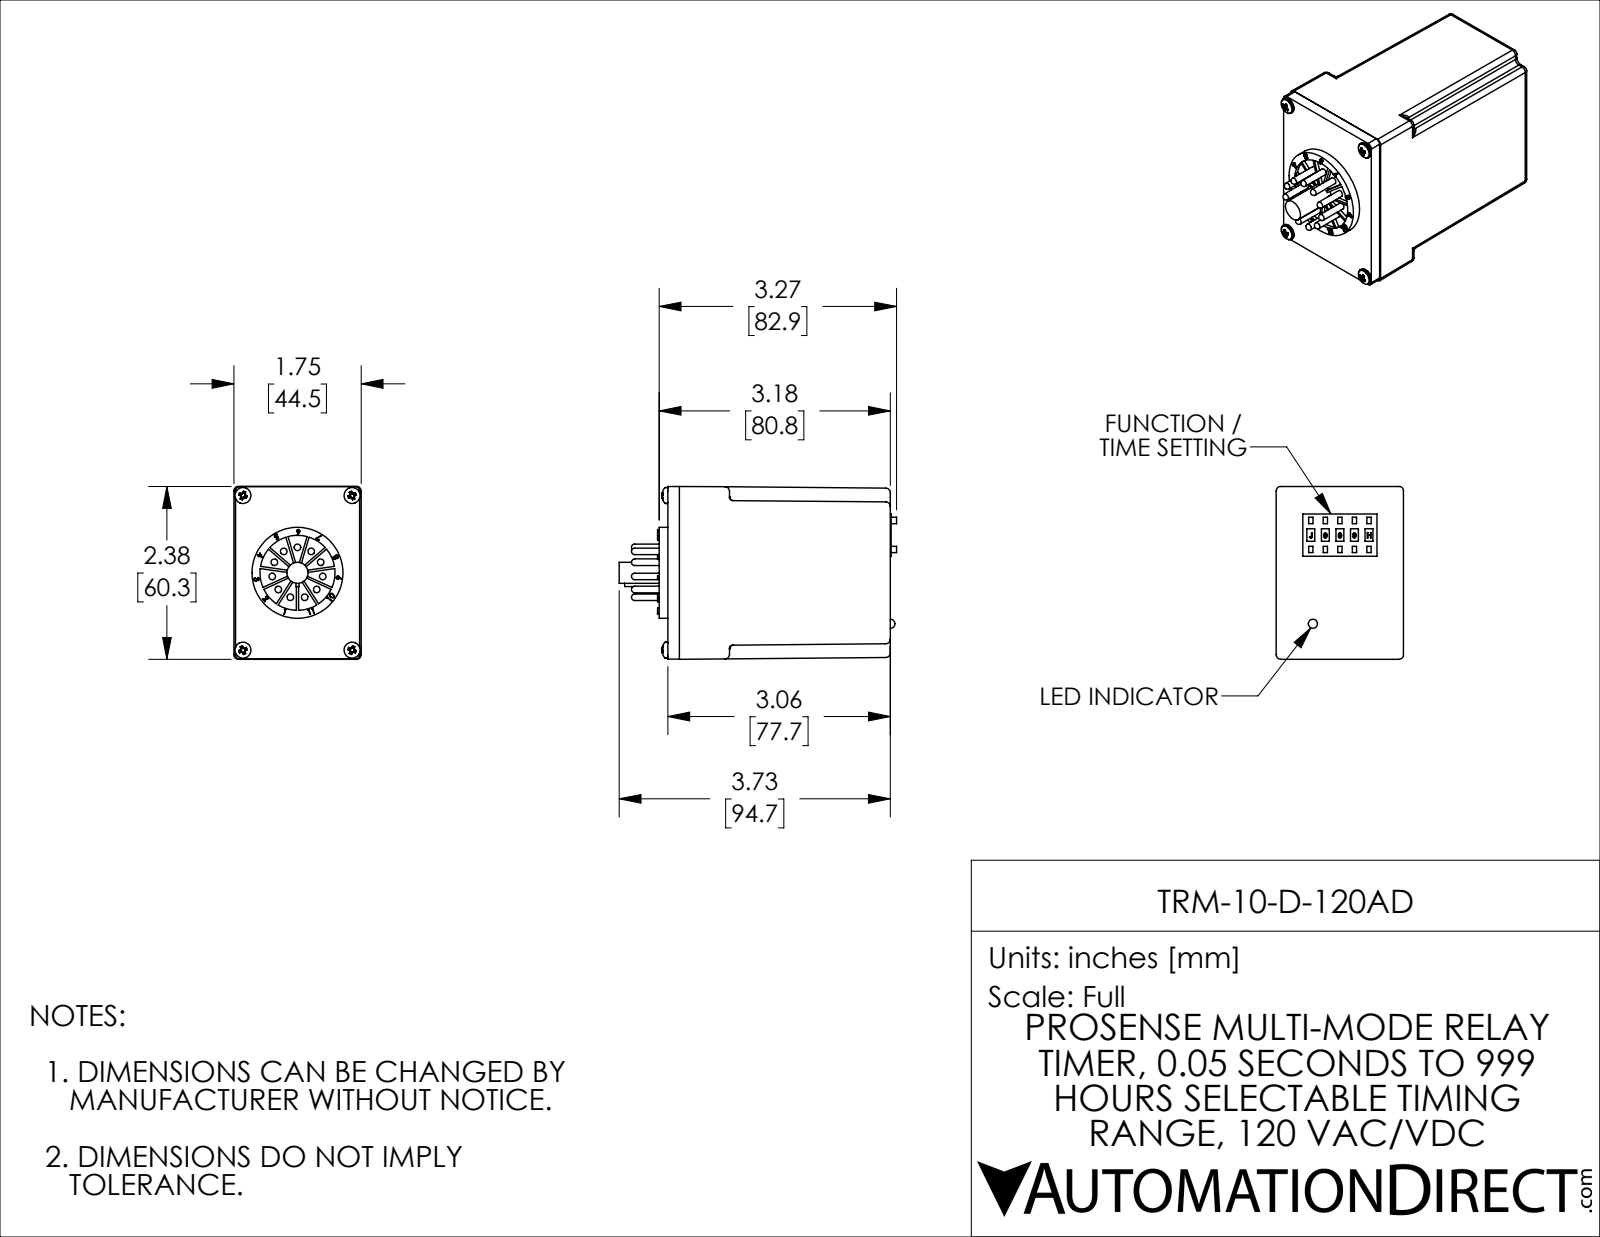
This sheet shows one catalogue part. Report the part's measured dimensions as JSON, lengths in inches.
{"part_name": "TRM-10-D-120AD", "step_written_by": "SolidWorks 2021 (CONFIG_CONTROL_DESIGN)", "units": "inches", "bodies": {"solids": 24, "faces": 740, "planar": 360, "cylindrical": 158, "other": 222}, "overall_size": [3.815, 2.375, 1.75], "volume_in3": 12.26, "surface_area_in2": 45.11, "round_holes": [[0.125, 4], [1.03, 1]], "round_bosses_or_shafts": [[0.09, 11], [0.219, 4], [1.25, 1], [0.29, 1]], "partial_cylinders_radius": [[0.063, 32], [0.05, 4]], "face_to_face_distances": [2.9, 0.16, 3.06, 0.07, 0.23, 3.13, 0.188, 0.05, 0.28, 0.12], "hole_center_spacings": [1.301, 1.5, 2.125, 2.601]}
